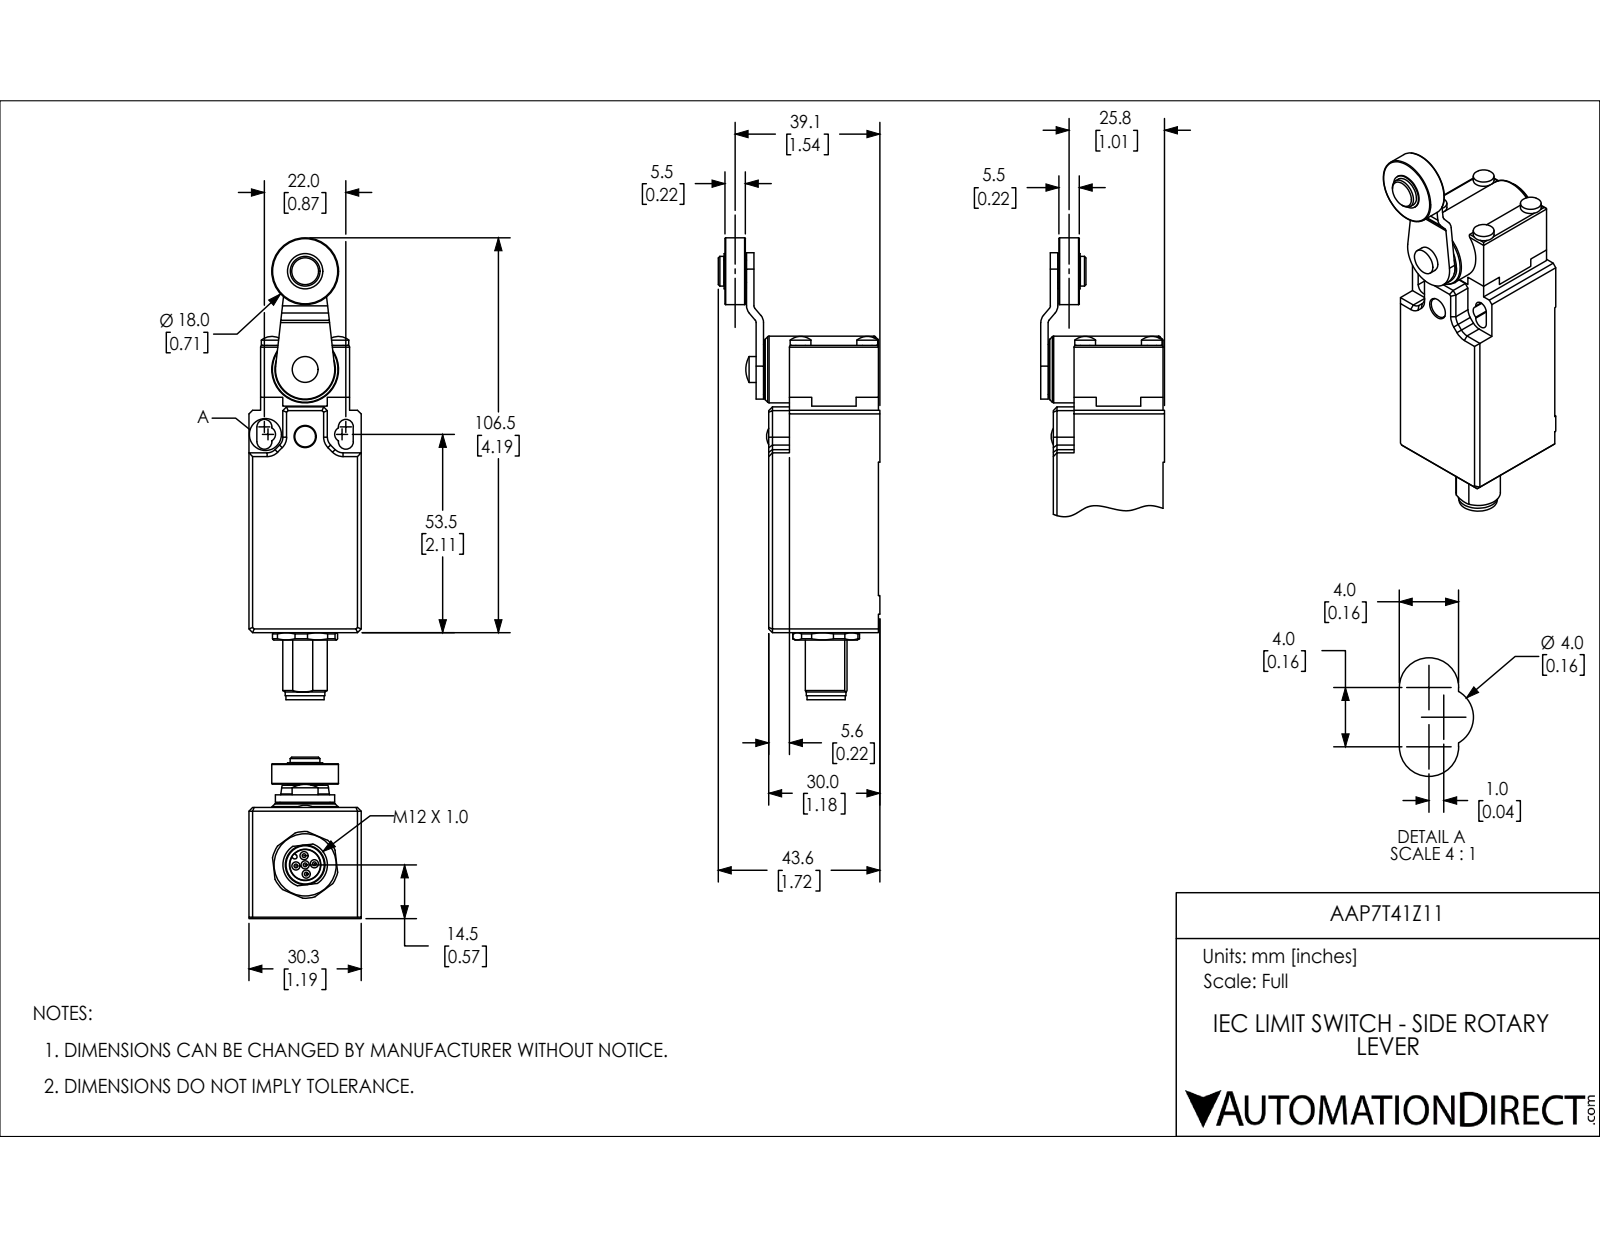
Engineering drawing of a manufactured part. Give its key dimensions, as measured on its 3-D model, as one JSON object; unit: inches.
{"part_name": "AAP7T41Z11", "step_written_by": "SolidWorks 2018 (AUTOMOTIVE_DESIGN)", "units": "inches", "bodies": {"solids": 4, "faces": 344, "planar": 151, "cylindrical": 131, "other": 62}, "overall_size": [4.906, 1.717, 1.193], "volume_in3": 4.191, "surface_area_in2": 28.22, "round_holes": [[0.087, 5], [0.236, 1], [0.512, 1], [0.551, 1], [0.63, 1]], "round_bosses_or_shafts": [[0.22, 5], [0.055, 5], [0.039, 5], [0.709, 2], [0.587, 1], [0.531, 1], [0.421, 1], [0.406, 1]], "partial_cylinders_radius": [[0.079, 6], [0.118, 6], [0.02, 4], [0.039, 2], [0.024, 1], [0.197, 1], [0.236, 1], [0.315, 1]], "face_to_face_distances": [1.193, 1.165, 0.124, 1.069, 0.945, 2.406, 0.276, 0.079, 0.236, 1.181], "hole_center_spacings": [0.098, 0.139, 0.196]}
